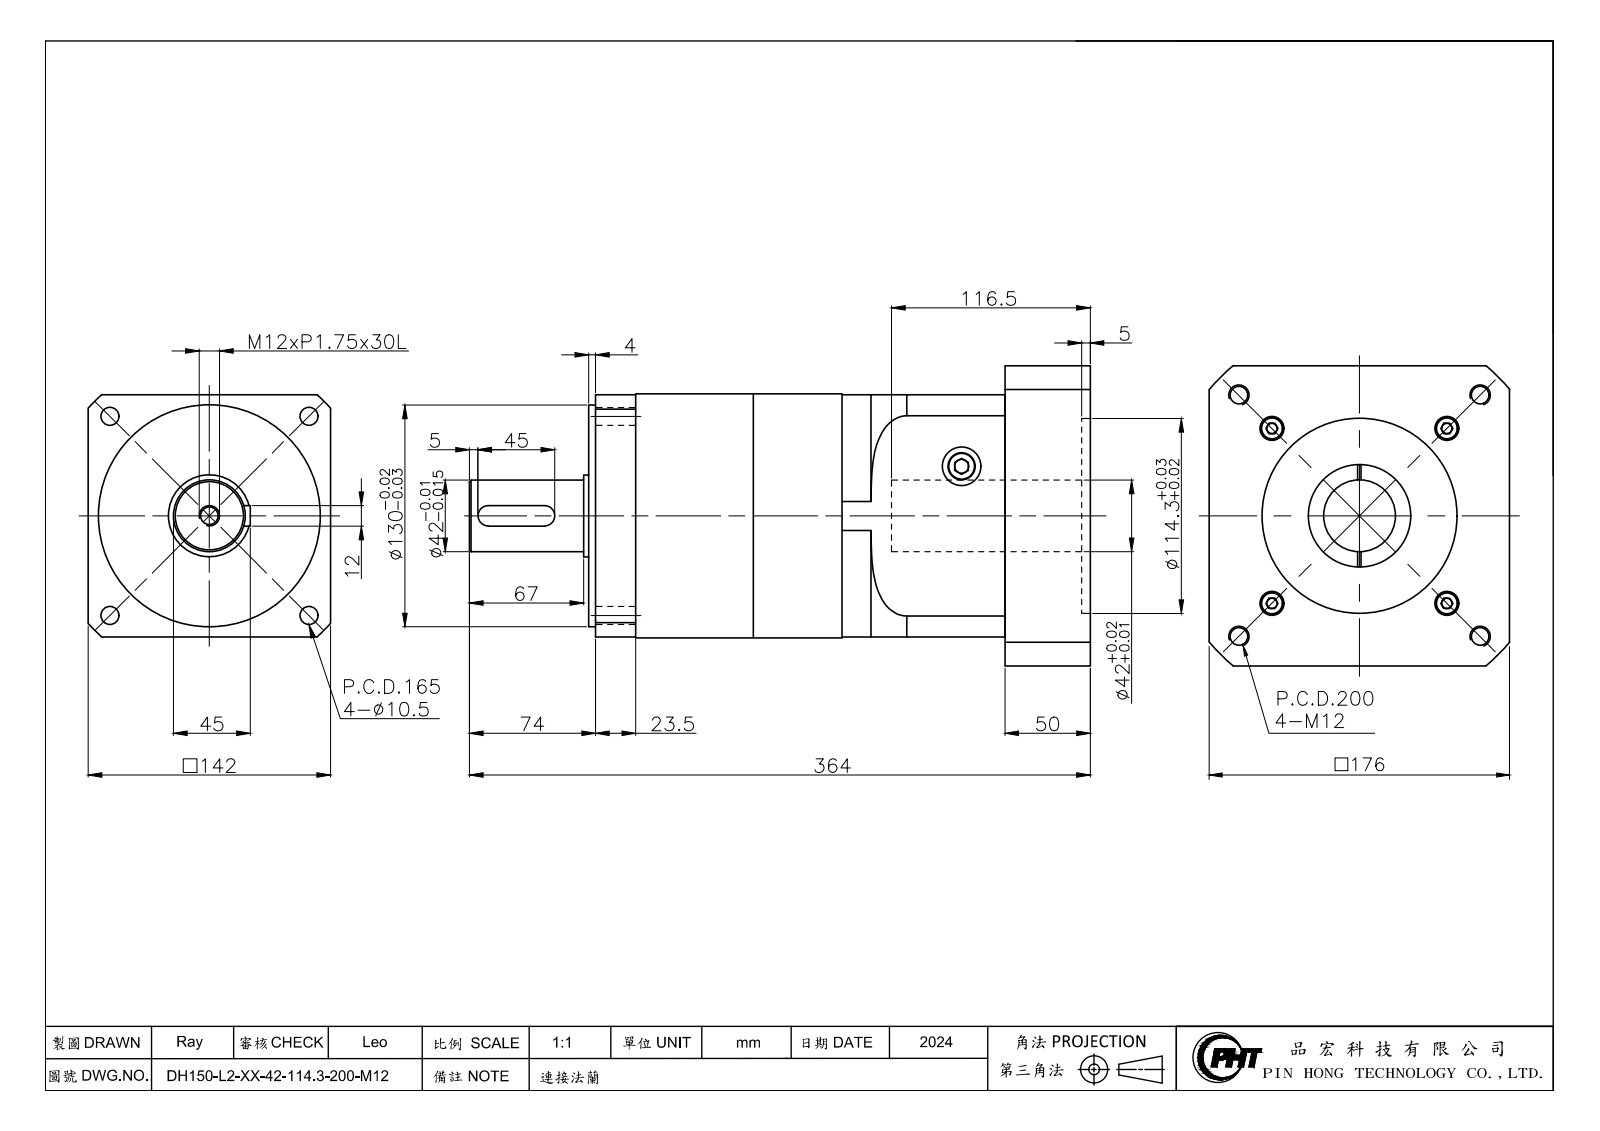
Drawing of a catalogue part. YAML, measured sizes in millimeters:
part_name: "DH150-L2-XX-42-114.3-200-M12(連接法蘭)_2024"
step_written_by: "SolidWorks 2016 (CONFIG_CONTROL_DESIGN)"
units: millimeters
bodies: {solids: 20, faces: 396, planar: 173, cylindrical: 159, other: 64}
overall_size: [364, 176, 176]
volume: 5386000
surface_area: 482477
round_holes:
  - {diameter: 14, count: 8}
  - {diameter: 10.2, count: 5}
  - {diameter: 6.8, count: 4}
  - {diameter: 9, count: 4}
  - {diameter: 10.5, count: 4}
  - {diameter: 15, count: 4}
  - {diameter: 22.5, count: 2}
  - {diameter: 42, count: 1}
  - {diameter: 60, count: 1}
  - {diameter: 92, count: 1}
  - {diameter: 110, count: 1}
  - {diameter: 114.3, count: 1}
round_bosses_or_shafts:
  - {diameter: 12.2, count: 12}
  - {diameter: 8, count: 12}
  - {diameter: 144, count: 1}
  - {diameter: 143, count: 1}
  - {diameter: 130, count: 1}
  - {diameter: 74, count: 1}
  - {diameter: 48, count: 1}
partial_cylinders:
  - {radius: 6, count: 2}
  - {radius: 92.5, count: 1}
  - {radius: 95, count: 1}
  - {radius: 115, count: 1}
face_to_face_distances: [121, 52, 69, 95.5, 147.5, 216.5, 16.5, 159.5, 143, 50]
hole_center_spacings: [66, 19.2, 25.37, 40.07, 84.48, 91.35, 93.34, 104.59]
